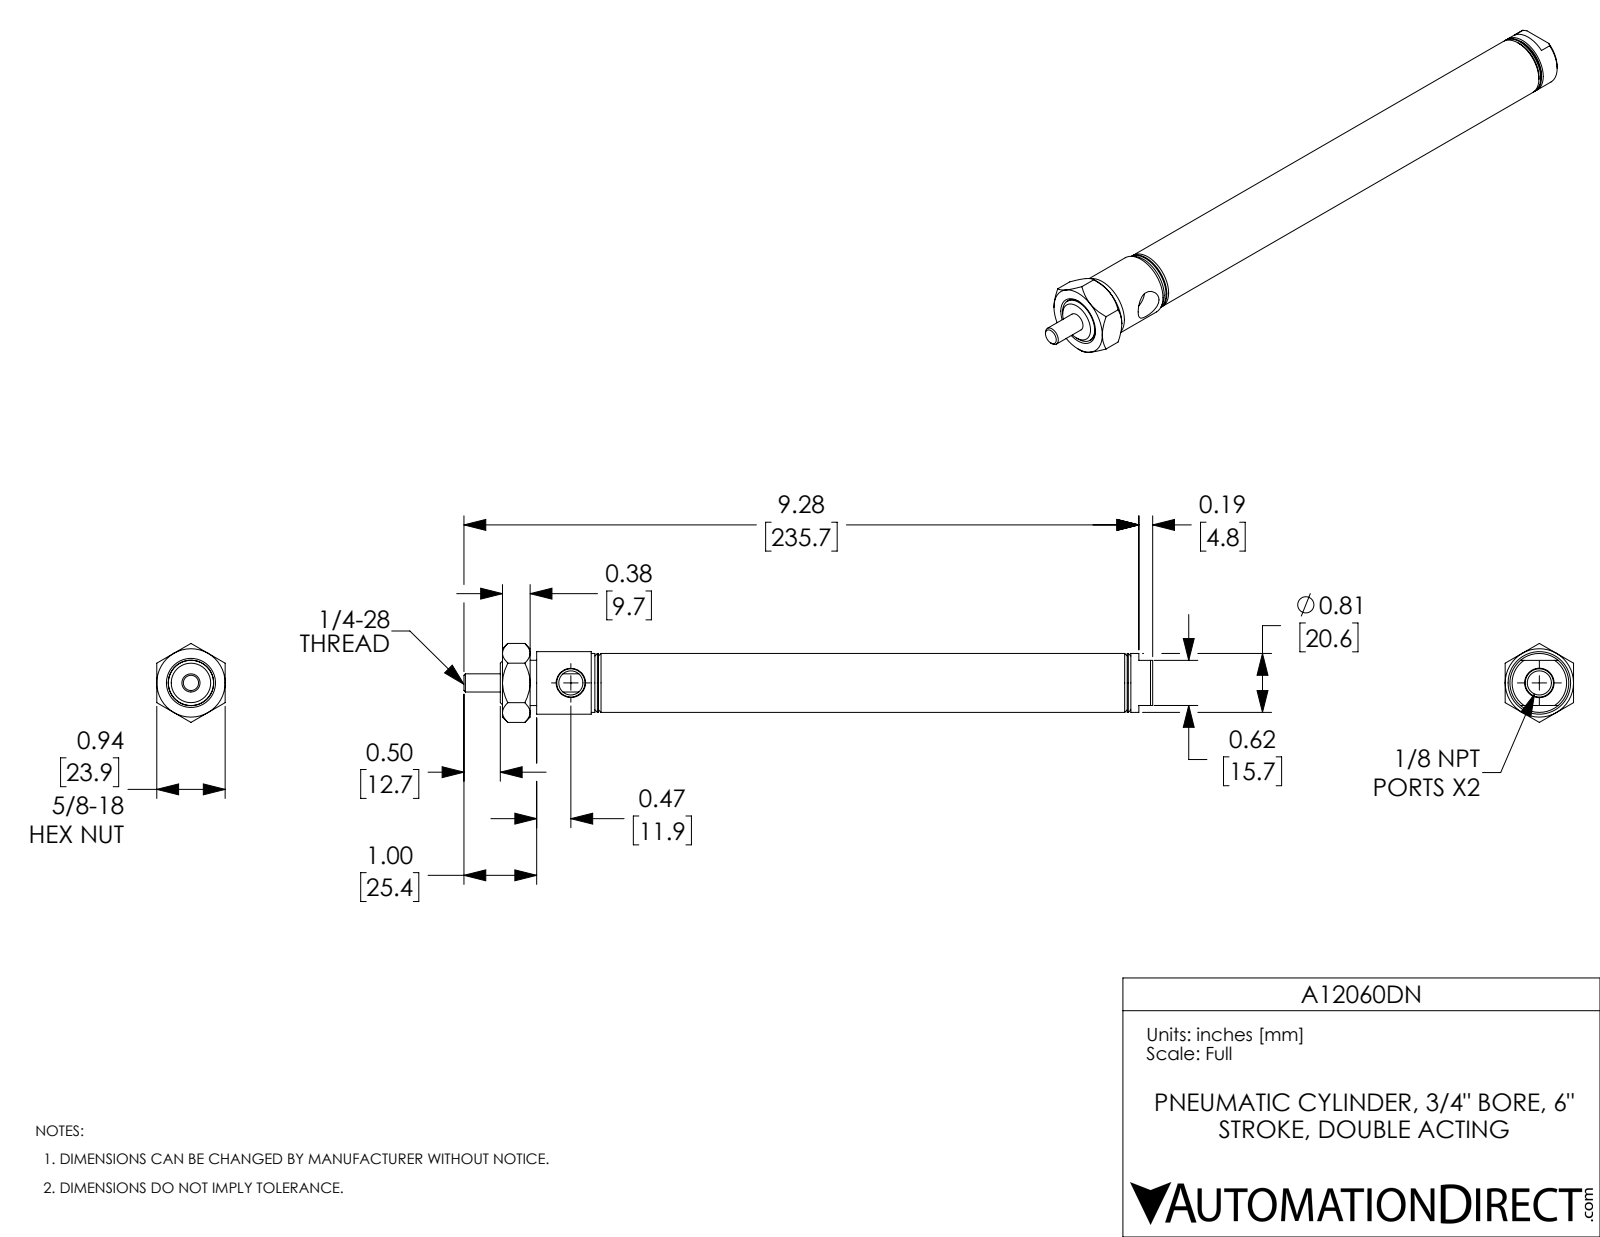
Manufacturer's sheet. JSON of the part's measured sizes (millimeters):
{"part_name": "A12060DN-MainBody; A12060DN-Rod; A12060DN_Mounting Nut_D-9; A12060DN", "step_written_by": "SolidWorks 2017 (AUTOMOTIVE_DESIGN)", "units": "millimeters", "bodies": {"solids": 3, "faces": 94, "planar": 27, "cylindrical": 28, "other": 39}, "overall_size": [240.5, 27.6, 23.9], "volume_mm3": 36850, "surface_area_mm2": 34610, "round_holes": [[8.4, 2], [6.4, 1], [15.9, 1], [19.1, 1]], "round_bosses_or_shafts": [[21.8, 1], [20.6, 1], [15.8, 1]], "face_to_face_distances": [190.1, 23.9, 12.7, 25, 37.7, 165.1, 152.4, 192.4, 179.7, 27.3]}
